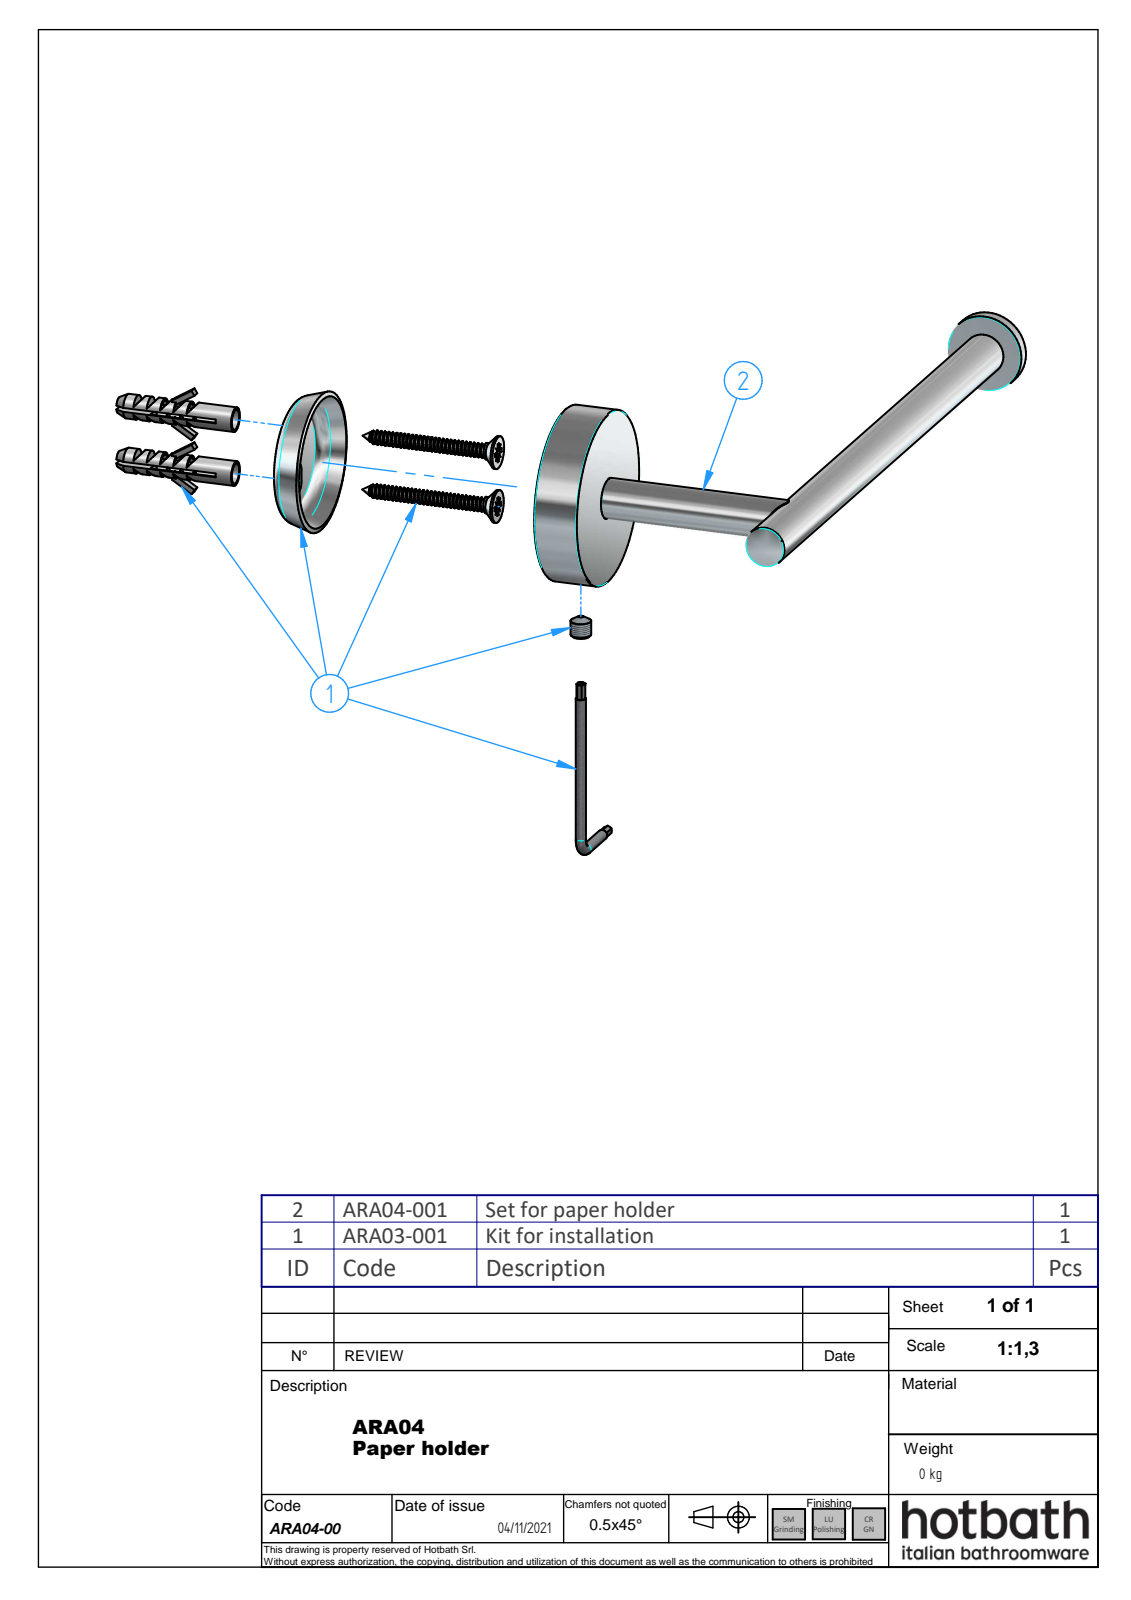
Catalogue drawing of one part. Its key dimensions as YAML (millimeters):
part_name: "ARA04-00; ARA04-001_oa_0; ARA03-01; ARA04-01 (+5 more)"
step_written_by: "ST-DEVELOPER v16.7 (AP242_MANAGED_MODEL_BASED_3D_ENGINEERING_MIM_LF)"
units: millimeters
bodies: {solids: 7, faces: 156, planar: 115, cylindrical: 21, other: 20}
overall_size: [155, 98.5, 43]
volume: 21486
surface_area: 15242
round_holes:
  - {diameter: 4.13, count: 2}
  - {diameter: 5, count: 2}
  - {diameter: 3, count: 1}
  - {diameter: 10, count: 1}
  - {diameter: 39.4, count: 1}
round_bosses_or_shafts:
  - {diameter: 6, count: 2}
  - {diameter: 43, count: 1}
  - {diameter: 19, count: 1}
  - {diameter: 10, count: 1}
  - {diameter: 5, count: 1}
partial_cylinders:
  - {radius: 4.35, count: 1}
  - {radius: 4.5, count: 1}
  - {radius: 17.8, count: 1}
face_to_face_distances: [1.4, 11, 9.6, 3.5, 1, 13.8, 2.48, 14.8, 12.8, 4.17]
hole_center_spacings: [5.65, 8.15, 13.8]
